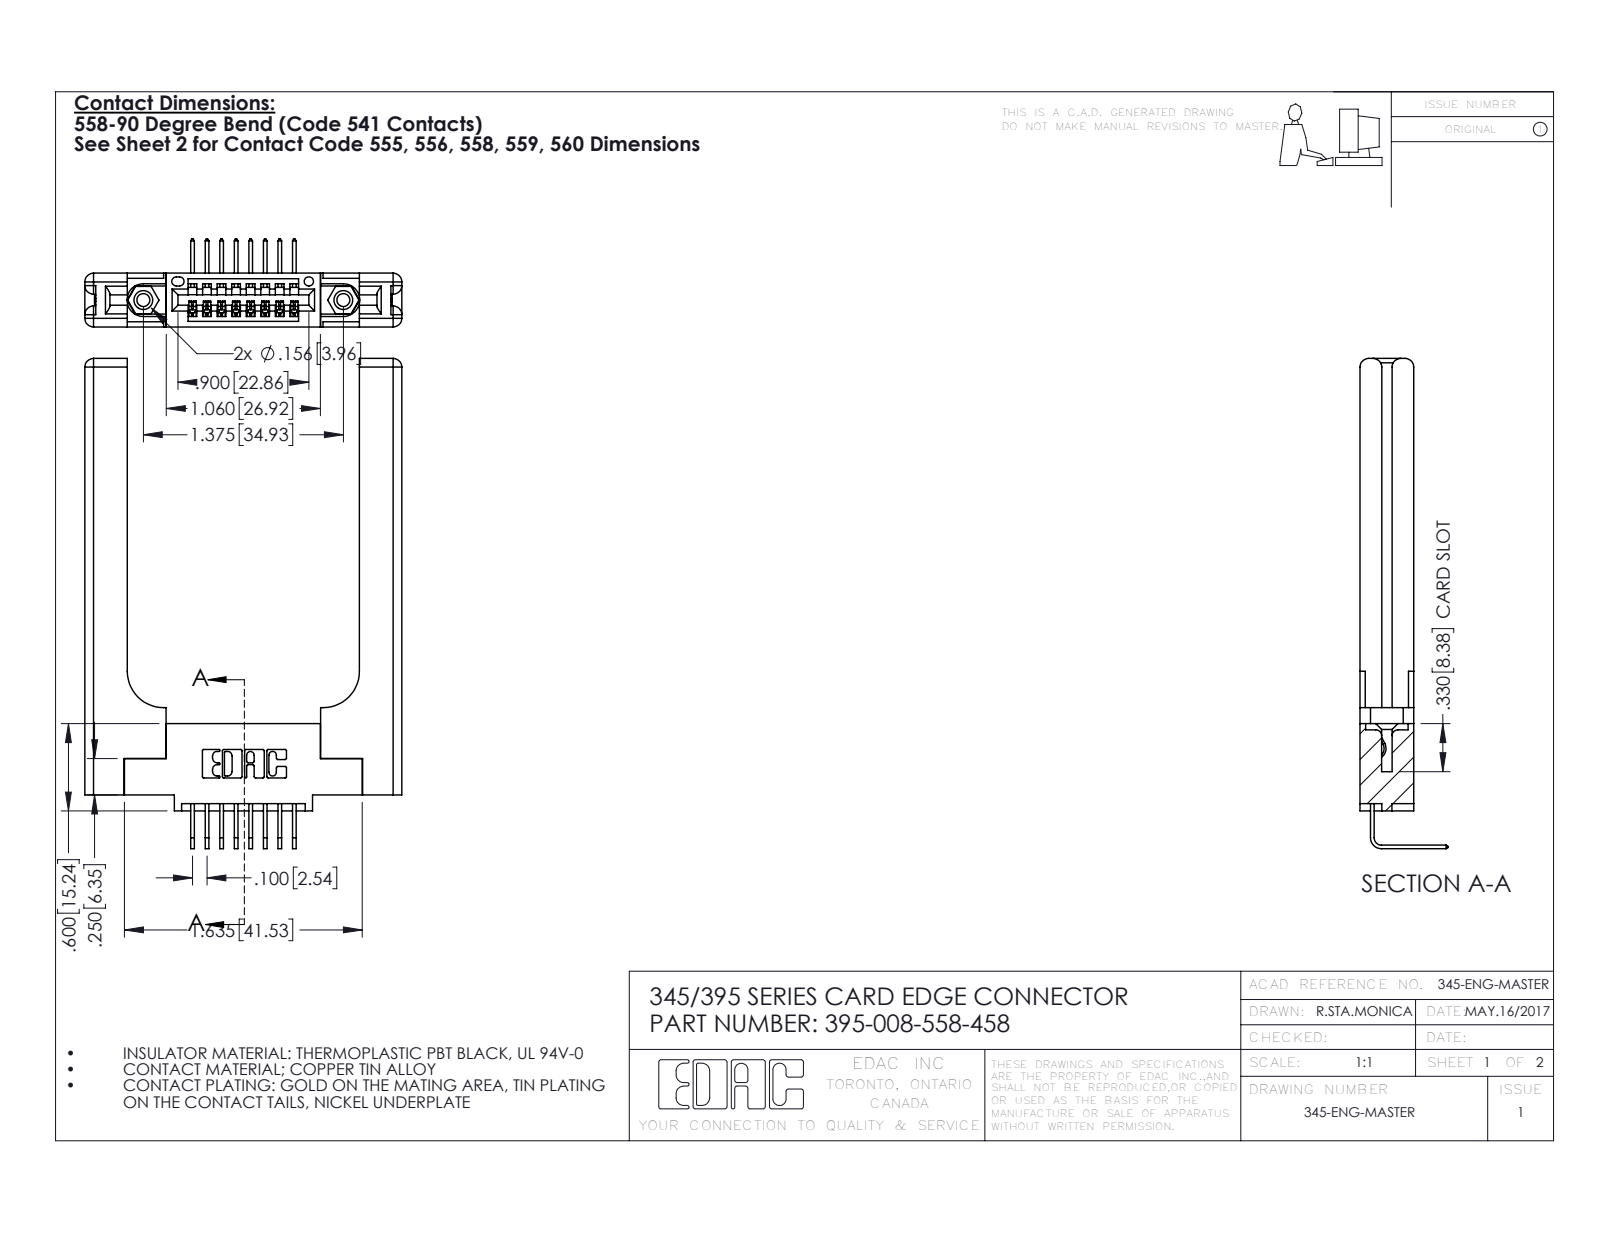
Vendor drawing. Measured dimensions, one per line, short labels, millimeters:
name: 345-220-058_345-220-058; 345-250-001_345-250-001-102; 345 Part_0.110 Offset - 0.156 Dia-TH; 345-292-001_558 Tail - 2 (+1 more)
written by: SolidWorks 2016 (CONFIG_CONTROL_DESIGN)
unit: mm
bodies: 13 solids, 866 faces (568 planar, 238 cylindrical, 60 other)
size: 85.6 × 55.3 × 15.4
volume: 13 400 mm³; area: 11 640 mm²
holes: 2× ⌀2.3, 2× ⌀3.2, 2× ⌀4, 1× ⌀1.6
bosses: 2× ⌀3.9
rounds: 22× R0.3, 16× R0.2, 16× R1.5, 6× R0.2, 6× R0.8, 3× R0.7, 2× R0.8, 2× R0.8
face distances: 9.4, 3.8, 5.6, 1.8, 3.8, 2, 7.6, 40.5, 1.8, 7.4
hole spacings: 6.9, 29.1, 34.9
